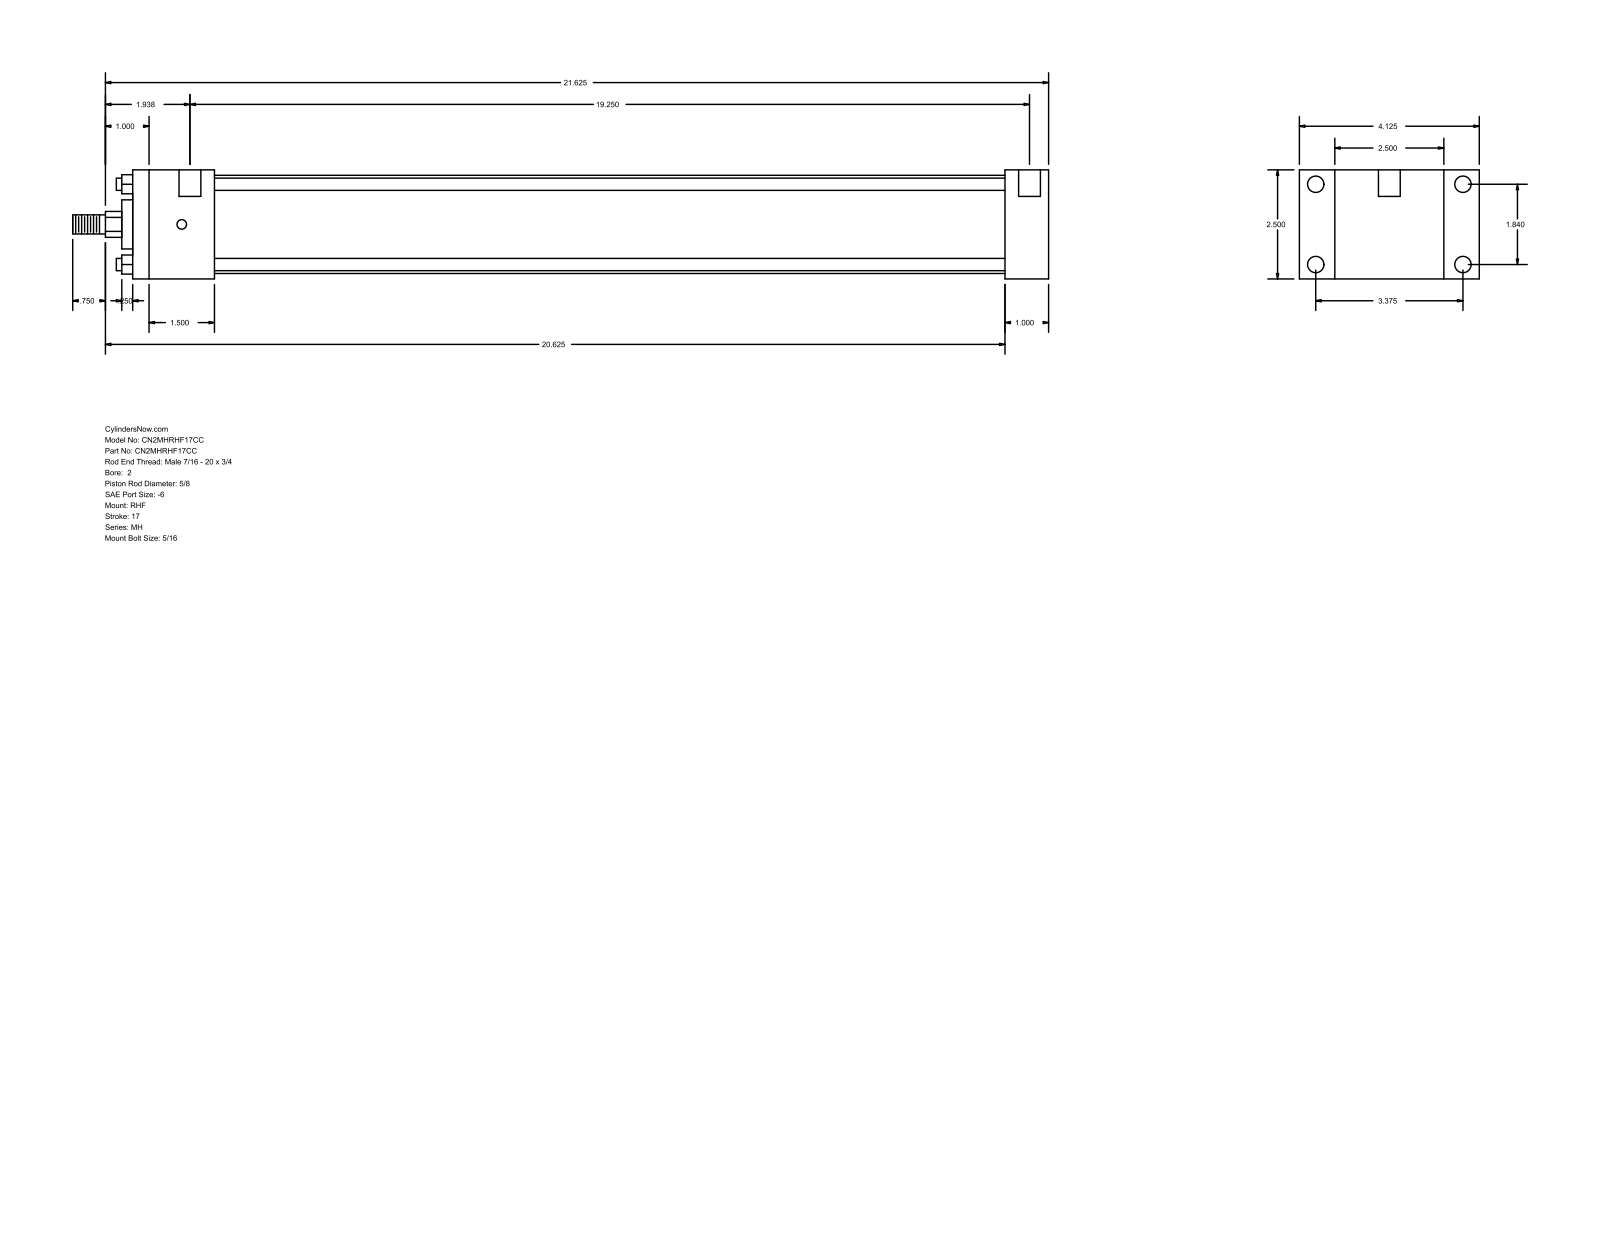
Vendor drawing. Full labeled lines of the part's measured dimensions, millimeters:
Part name (STEP PRODUCT): MH_RHF__0200_0.625
STEP written by: GSSL Pune (CONFIG_CONTROL_DESIGN)
Units: millimetres
Bodies: 0 solids, 88 faces (60 planar, 28 cylindrical, 0 other)
Overall size (bounding box): 568.33 × 104.78 × 63.5
Round holes (diameter × count): ⌀5.56 ×4, ⌀9.53 ×4, ⌀12.7 ×2
Round bosses / shafts (diameter × count): ⌀7.14 ×4, ⌀57.15 ×1, ⌀28.57 ×1, ⌀15.88 ×1, ⌀11.11 ×1
Partial cylindrical surfaces — rounded edges, fillets, slot ends (radius × count): R7.54 ×1
Main face-to-face distances: 63.5, 25.39, 20.64, 84.14, 508, 533.39, 104.78, 47.62, 460.38, 485.77
Hole centre spacings: 46.74, 85.72, 97.63, 496.89, 3.18, 4.76, 488.95, 492.13
